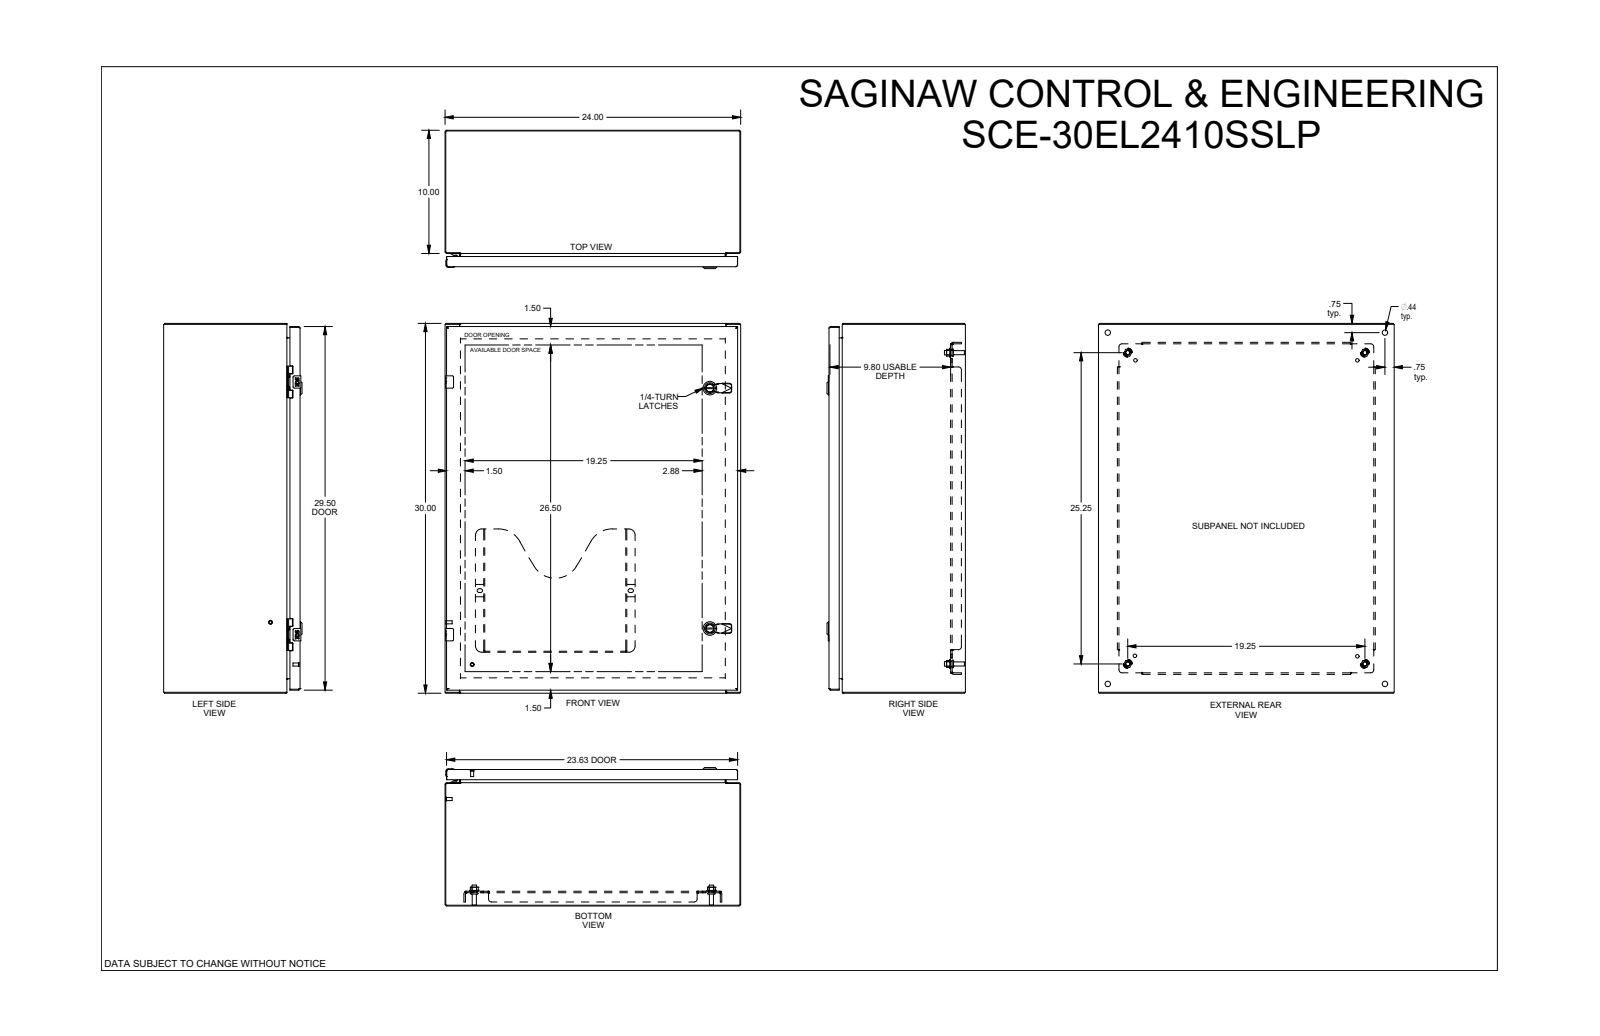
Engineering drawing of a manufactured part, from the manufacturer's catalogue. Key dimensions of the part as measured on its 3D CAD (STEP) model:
Part name (STEP PRODUCT): SCE-30EL2410SSLP
STEP written by: SolidWorks 2019 (CONFIG_CONTROL_DESIGN)
Units: inches
Bodies: 0 solids, 2838 faces (1307 planar, 759 cylindrical, 772 other)
Overall size (bounding box): 30 × 24 × 11.23
Round holes (diameter × count): ⌀0.172 ×4, ⌀0.205 ×4, ⌀0.244 ×4, ⌀0.266 ×4, ⌀0.281 ×4, ⌀0.367 ×4, ⌀0.437 ×4, ⌀0.5 ×4, ⌀0.375 ×3, ⌀0.156 ×2, ⌀0.197 ×2, ⌀0.218 ×2
Round bosses / shafts (diameter × count): ⌀0.17 ×6, ⌀0.366 ×4, ⌀0.332 ×4, ⌀0.25 ×4, ⌀0.248 ×4, ⌀0.196 ×3, ⌀1.102 ×2, ⌀0.866 ×2
Partial cylindrical surfaces — rounded edges, fillets, slot ends (radius × count): R0.012 ×56, R0.015 ×32, R0.01 ×28, R0.04 ×23, R0.02 ×20, R0.029 ×12, R0.07 ×10, R0.145 ×10
Main face-to-face distances: 0.075, 0.075, 10.923, 10.998, 11.073, 10.998, 1.2, 9.873, 23.925, 1
Hole centre spacings: 20.5, 0.985, 0.02, 0.875, 4.493, 20.938, 3.173, 18.641
